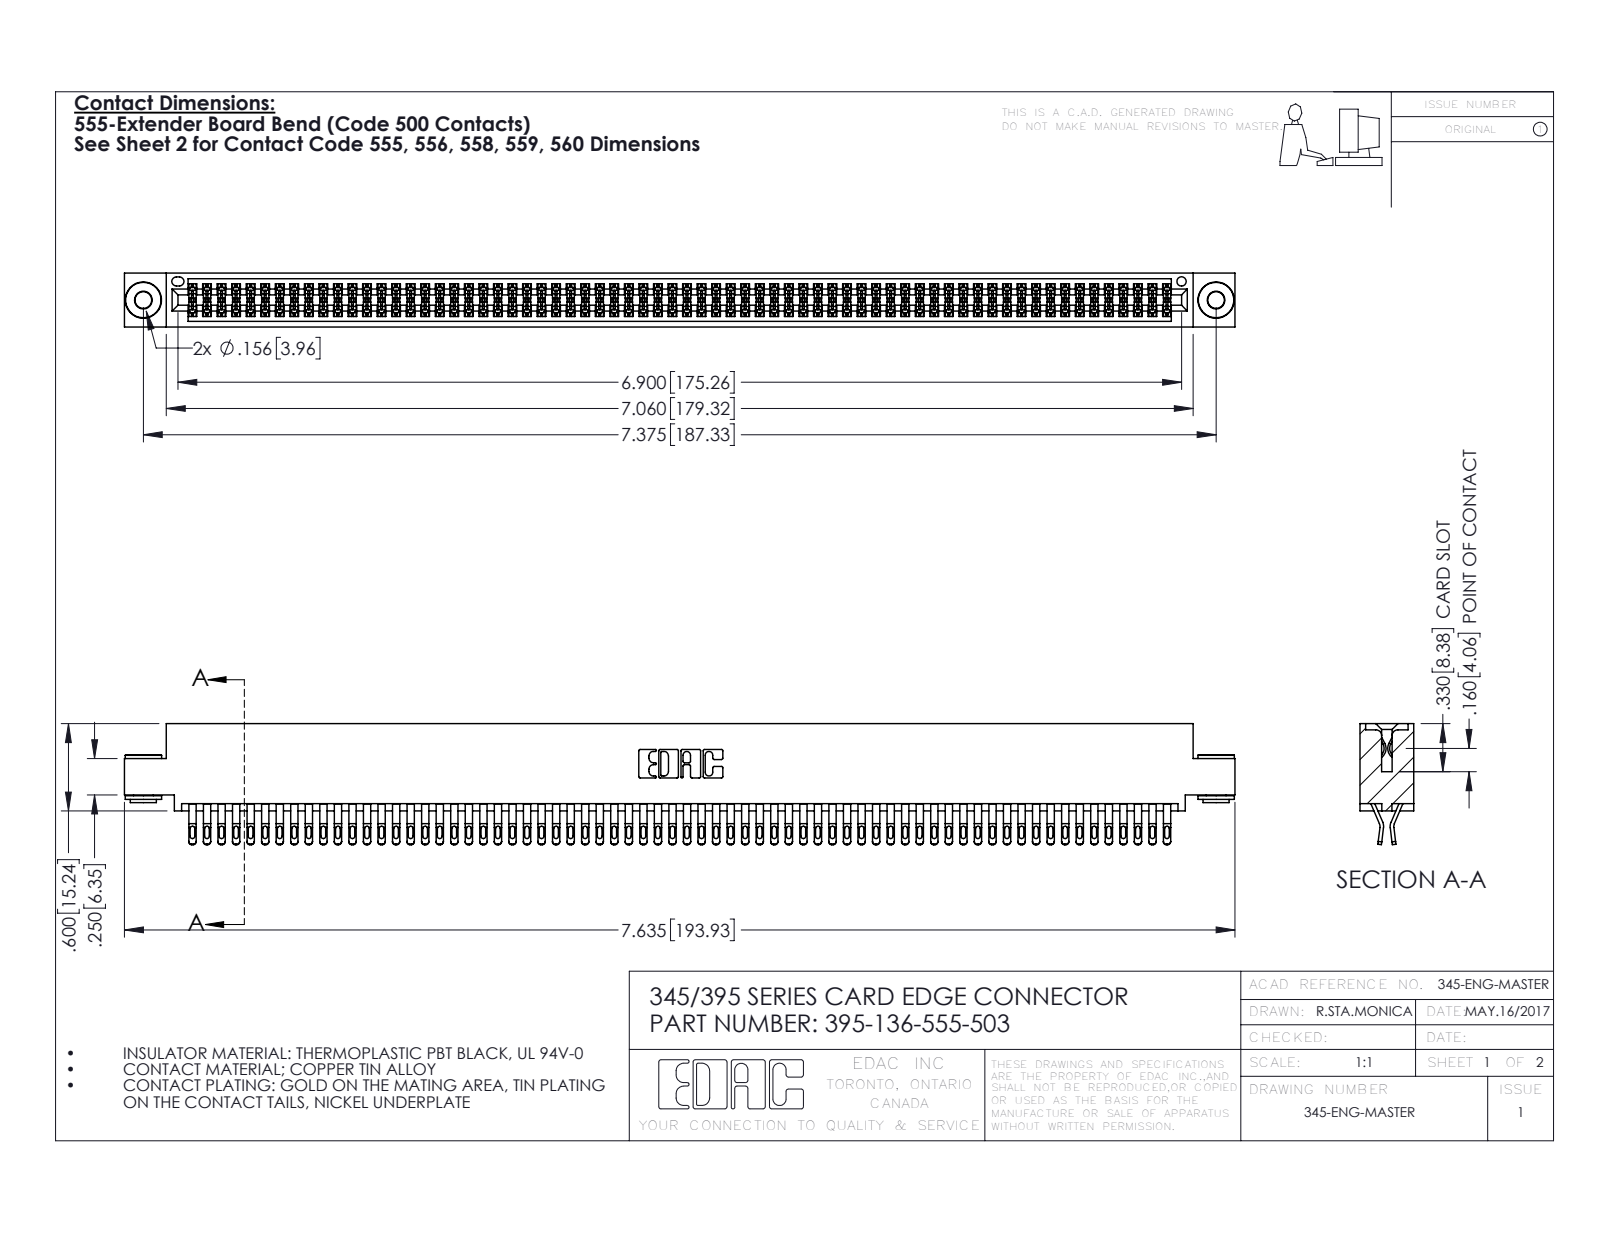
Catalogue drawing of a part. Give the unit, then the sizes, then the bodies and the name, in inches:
Units: inches
Overall size (bounding box): 7.635 × 0.832 × 0.37
Round holes (diameter × count): ⌀0.116 ×2, ⌀0.156 ×2, ⌀0.064 ×1
Round bosses / shafts (diameter × count): ⌀0.25 ×2, ⌀0.18 ×2, ⌀0.136 ×2
Partial cylindrical surfaces — rounded edges, fillets, slot ends (radius × count): R0.016 ×340, R0.02 ×272, R0.006 ×204, R0.01 ×22, R0.007 ×6, R0.031 ×6, R0.026 ×3, R0.01 ×2
Main face-to-face distances: 0.072, 0.298, 0.025, 0.37, 0.2, 0.098, 0.272, 0.225, 0.175, 0.149
Hole centre spacings: 0.27, 7.139, 7.375
Volume: 1.185 in³ · Surface area: 47.86 in²
Bodies: 139 solids, 7784 faces (4310 planar, 3466 cylindrical, 8 other)
Part name (STEP PRODUCT): 345 Part_0.110 Offset - 0.156 Dia-TH; 345-250-002_345-250-002-102; 395-136-555-503; 345-292-001_555 Tail
STEP written by: SolidWorks 2016 (CONFIG_CONTROL_DESIGN)
